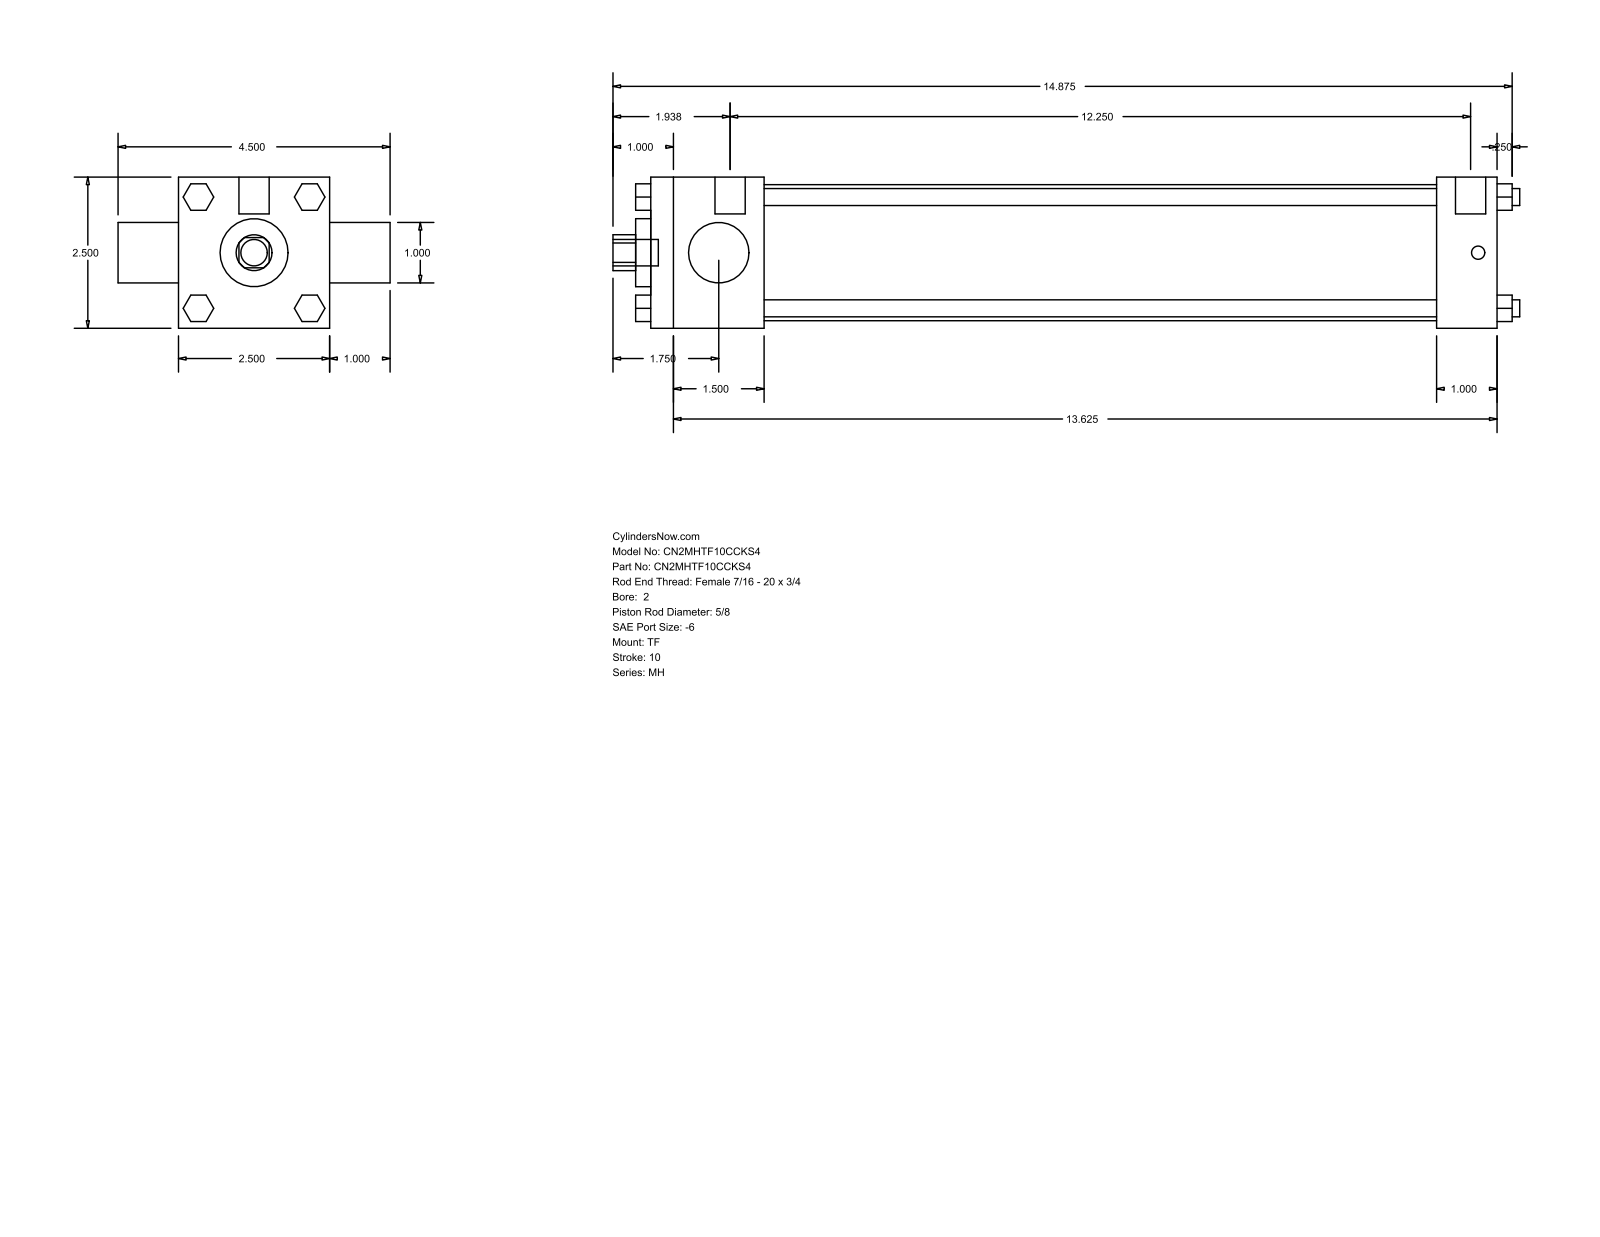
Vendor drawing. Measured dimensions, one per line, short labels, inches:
name: MH_TF__0200_0.625
written by: GSSL Pune (CONFIG_CONTROL_DESIGN)
unit: in
bodies: 0 solids, 120 faces (92 planar, 28 cylindrical, 0 other)
size: 15 × 4.5 × 2.5
holes: 1× ⌀0.625, 1× ⌀1, 1× ⌀1.125, 1× ⌀2.25
bosses: 4× ⌀0.281, 3× ⌀0.219, 2× ⌀0.5, 1× ⌀0.437
rounds: 1× R0.297
face distances: 2.5, 14, 1.875, 13, 11.125, 12.125, 1, 1, 3.5, 14.25
